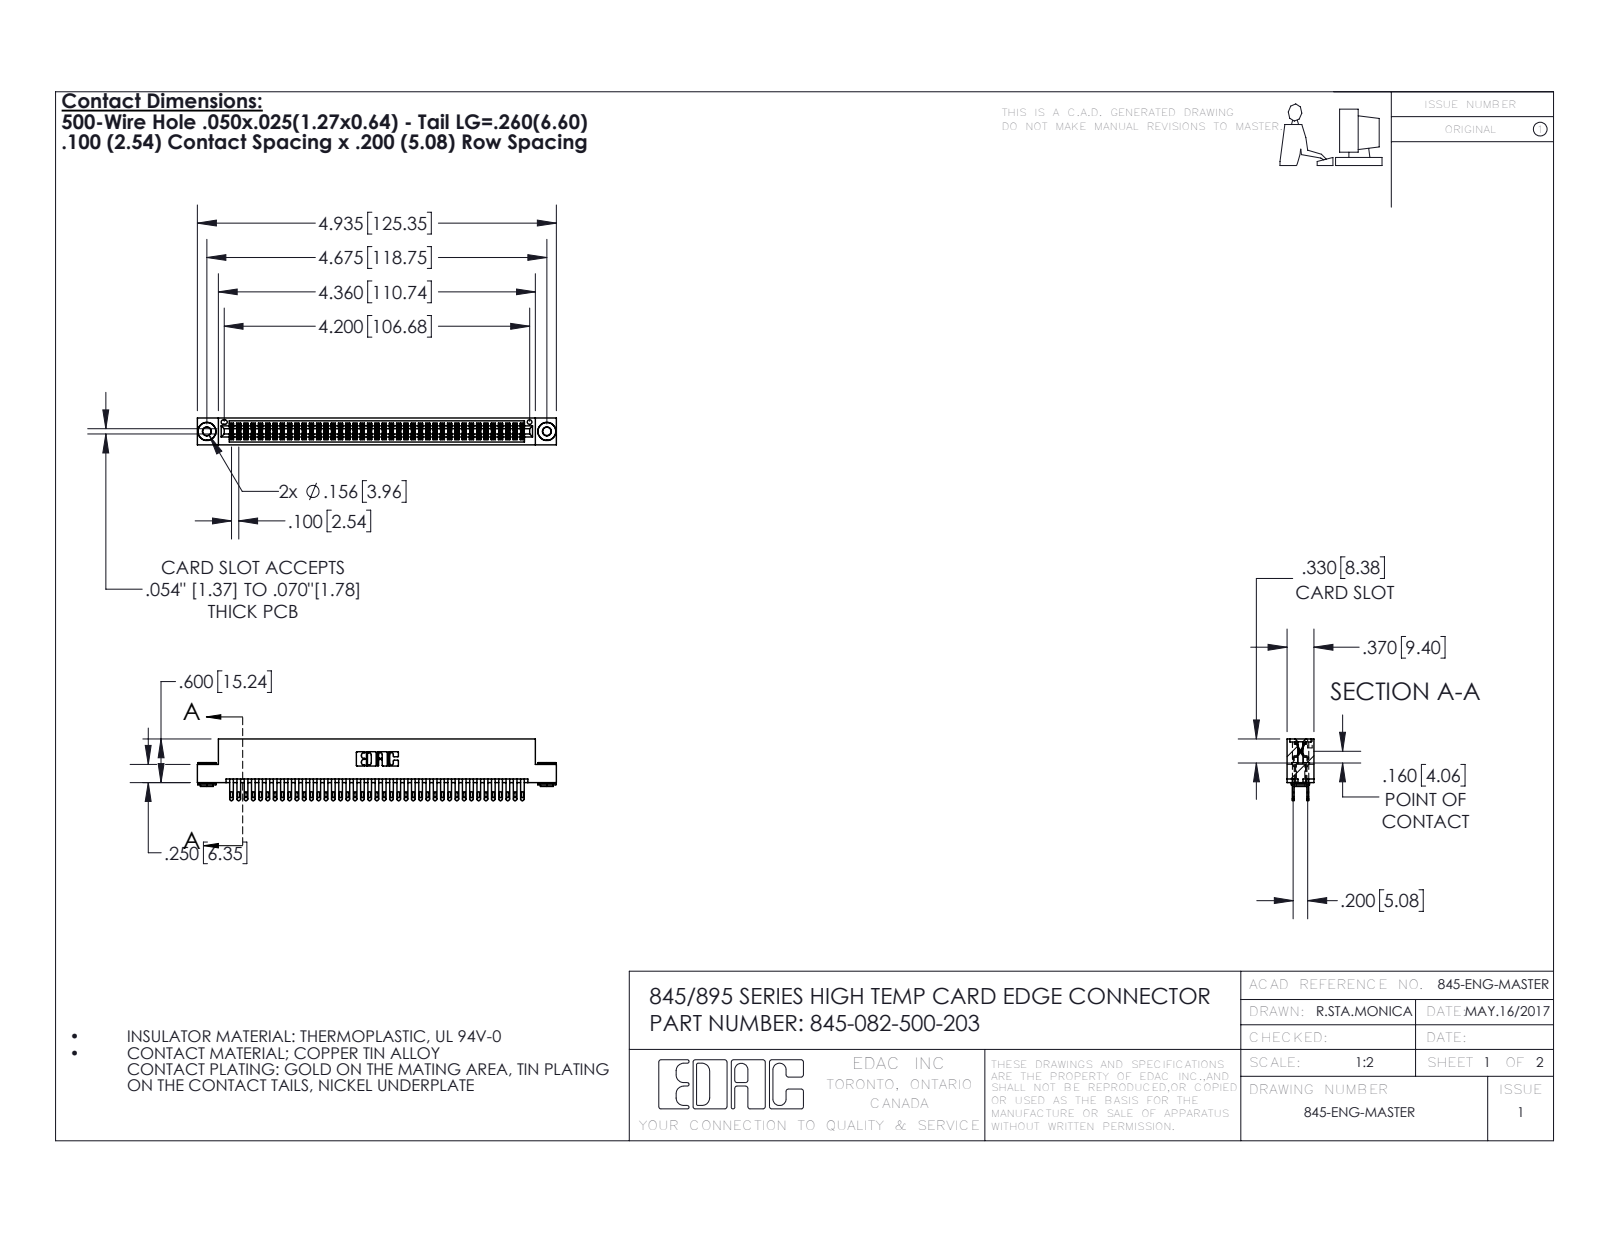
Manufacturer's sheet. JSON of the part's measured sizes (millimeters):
{"part_name": "345-292-001_345-293-100; 345-250-002_345-250-002-102; 345-082-500-203; 345 Part_Flush Mounting Lugs - 0.156 Dia-TH", "step_written_by": "SolidWorks 2016 (CONFIG_CONTROL_DESIGN)", "units": "millimeters", "bodies": {"solids": 85, "faces": 3936, "planar": 2304, "cylindrical": 1624, "other": 8}, "overall_size": [125.3, 21.5, 9.4], "volume_mm3": 12400, "surface_area_mm2": 19410, "round_holes": [[2.9, 2], [4, 2], [1.6, 1]], "round_bosses_or_shafts": [[6.4, 2], [4.6, 2], [3.5, 2]], "partial_cylinders_radius": [[0.2, 123], [0.4, 82], [0.5, 82], [0.3, 22], [0.2, 6], [0.8, 6], [0.7, 3], [0.4, 2]], "face_to_face_distances": [1.8, 7.6, 5.1, 0.6, 2.5, 6.9, 9.4, 5.7, 4.4, 3.8], "hole_center_spacings": [6.9, 112.8, 118.7]}
